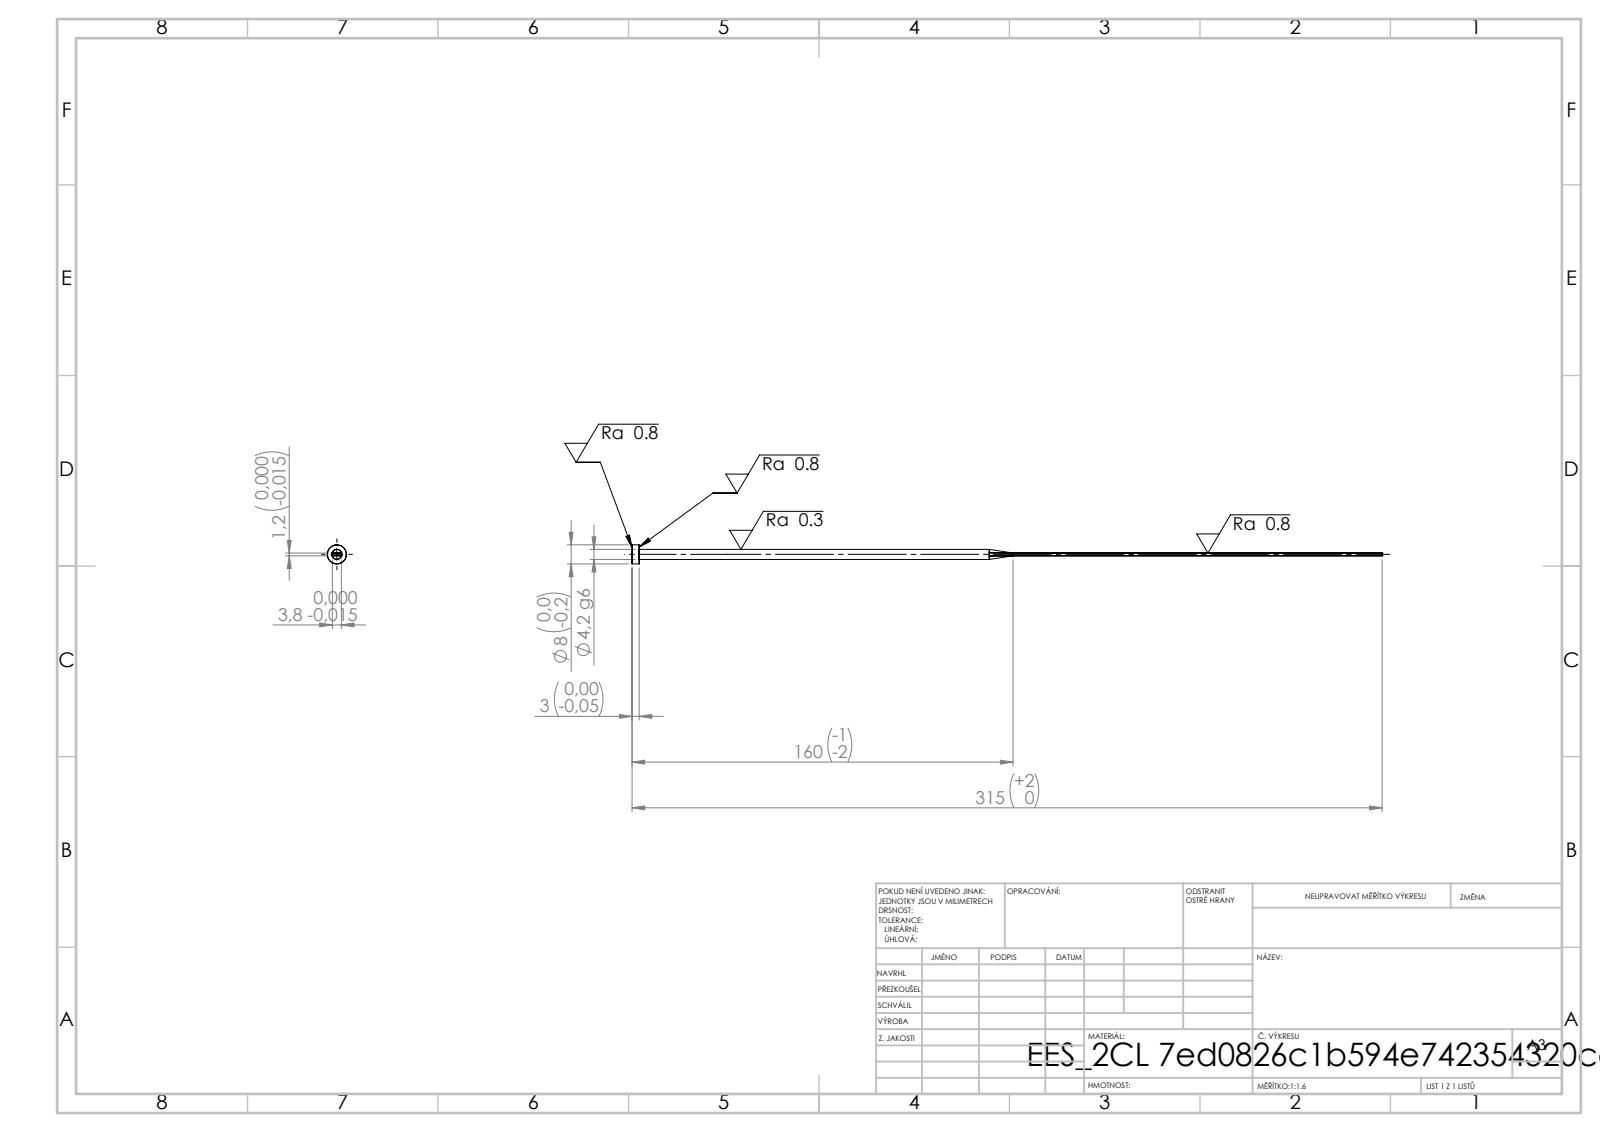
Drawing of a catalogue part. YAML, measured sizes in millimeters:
step_written_by: "SolidWorks 2019 (CONFIG_CONTROL_DESIGN)"
units: millimeters
bodies: {solids: 1, faces: 15, planar: 7, cylindrical: 4, other: 4}
overall_size: [315, 8, 8]
volume: 2983
surface_area: 3769
round_bosses_or_shafts:
  - {diameter: 8, count: 1}
  - {diameter: 4.2, count: 1}
face_to_face_distances: [1.2, 3.8, 3, 315, 312]
